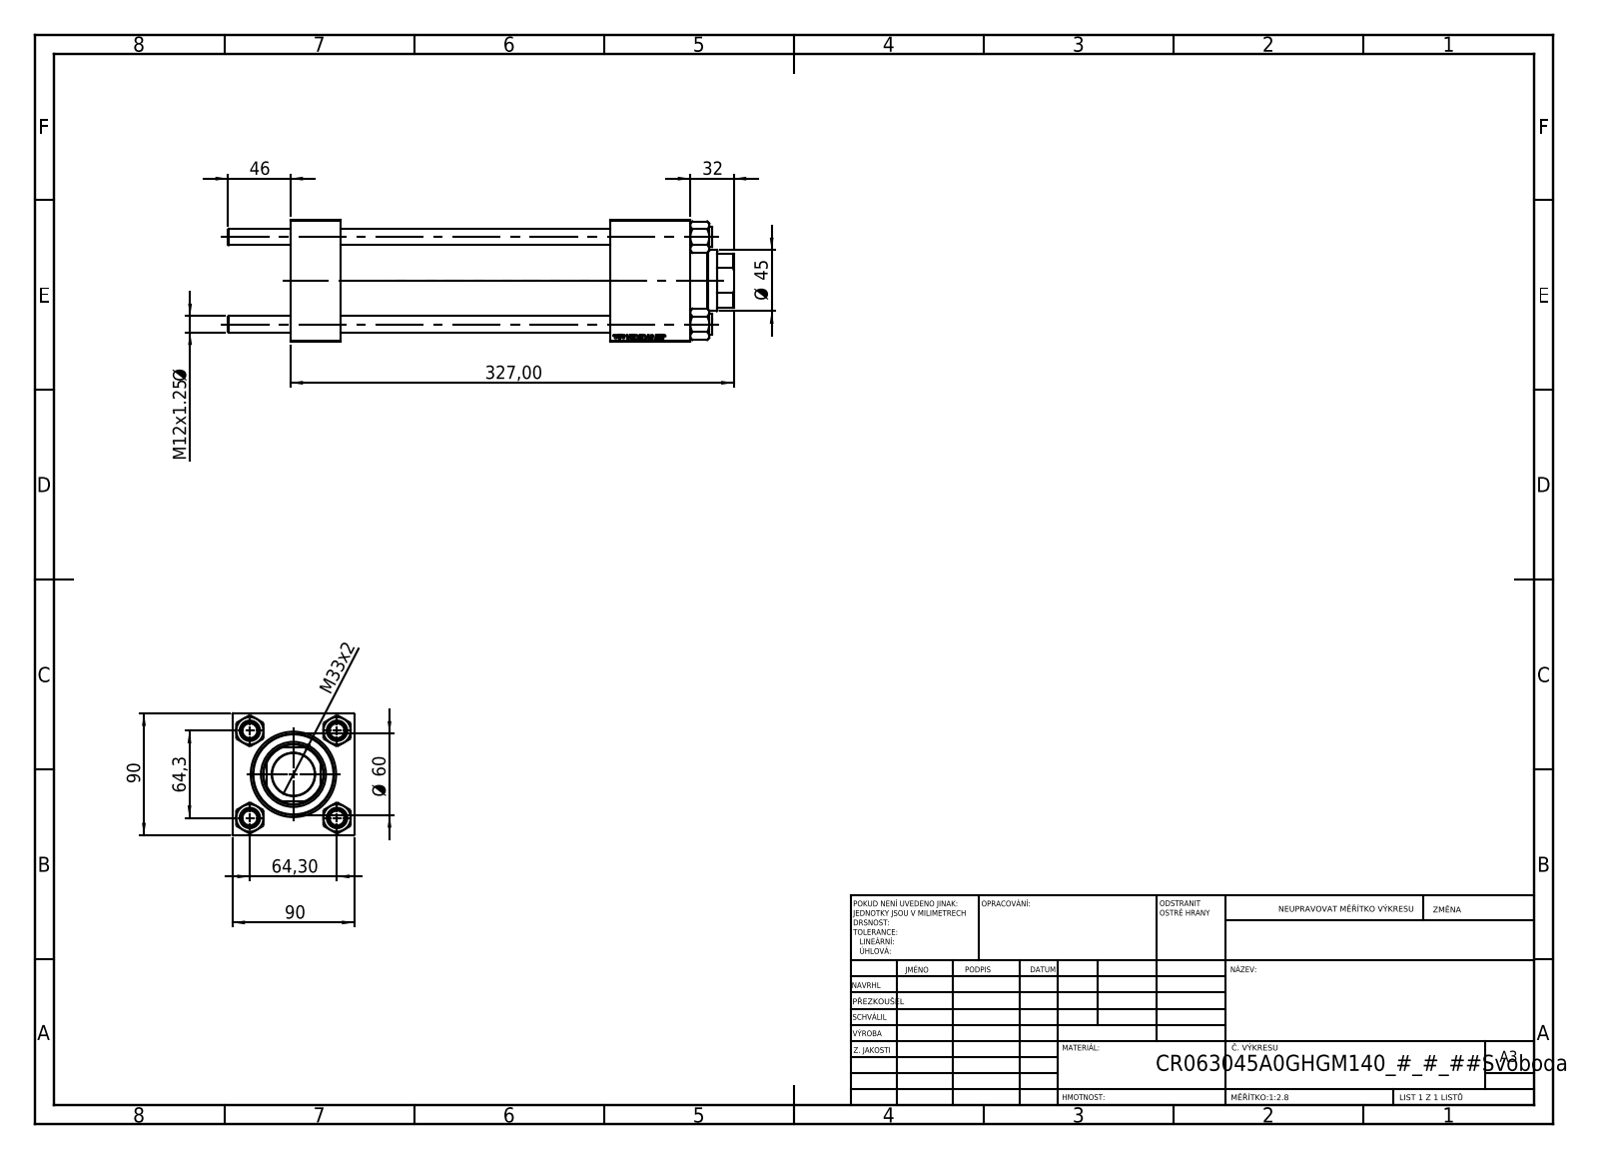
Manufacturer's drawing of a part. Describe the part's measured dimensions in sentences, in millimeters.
The part is named "V215CR_VCP; V215_VC_A; NUT_M5; CR025_012_A_0_G_A_G_M_020_+#_##_TYCINKA (+1 more)". Its 3-D file was written by "SolidWorks 2019 (CONFIG_CONTROL_DESIGN)". It is 11 solids with 1131 faces: 519 planar, 76 cylindrical and 536 other. Overall it measures 373 by 90 by 90 millimeters. Its volume is 1 405 000 cubic millimeters and its surface area 305 026 square millimeters. Round holes: 4 of diameter 12, 2 of diameter 7, 2 of diameter 20.96, 2 of diameter 30, 1 of diameter 31.5, 1 of diameter 45, 1 of diameter 48, 1 of diameter 50, 1 of diameter 60, 1 of diameter 63. Round bosses or shafts: 4 of diameter 15, 1 of diameter 69. Partial cylindrical surfaces (rounded edges, fillets, slot ends): 1 of radius 22. The main face-to-face distances are 90, 37, 295, 258, 236, 199, 59, 266.3, 229.3, 30.3. The hole center spacings are 45.47, 64.3, 90.93, 237.5.
